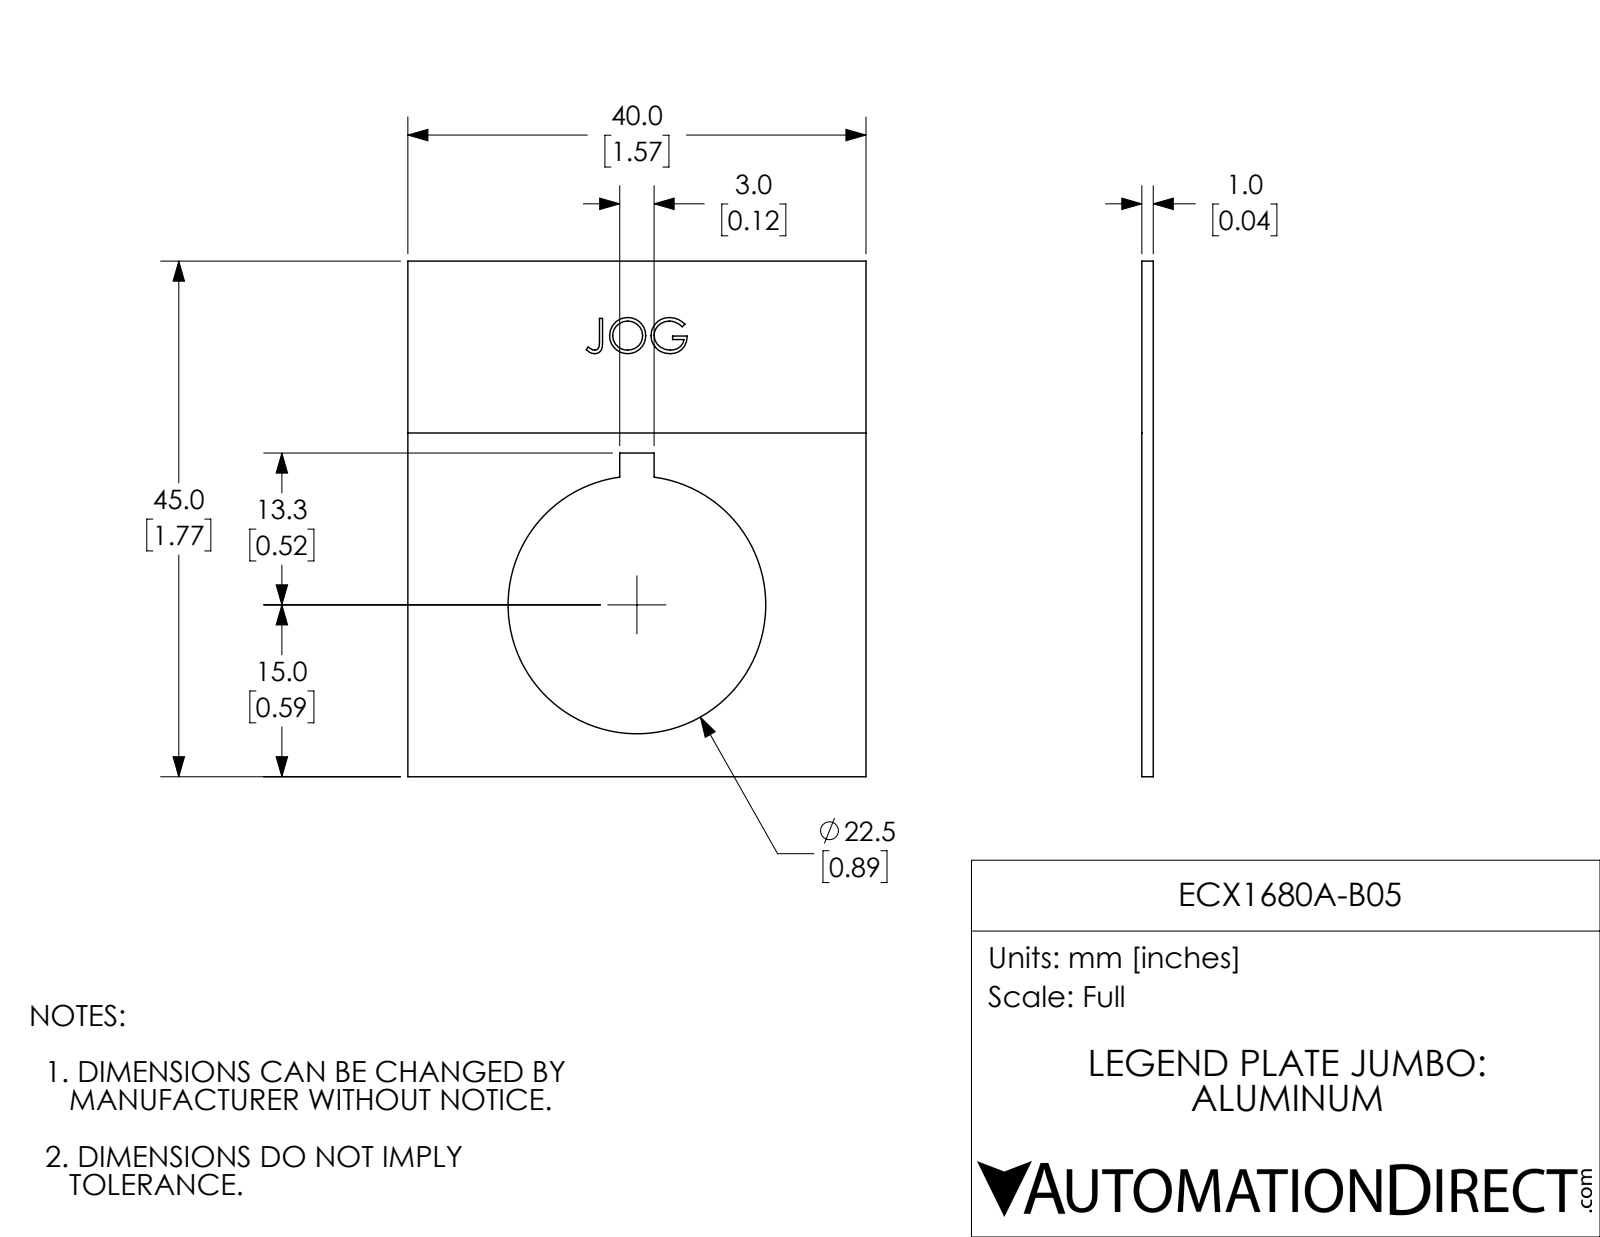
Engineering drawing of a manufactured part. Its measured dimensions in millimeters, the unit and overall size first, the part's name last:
Units: millimetres
Overall size (bounding box): 45 × 40 × 1
Round holes (diameter × count): ⌀22.5 ×1
Main face-to-face distances: 1, 0.99, 40, 45, 18.5, 21.5, 28.25, 16.75, 3, 30
Volume: 1 393 mm³ · Surface area: 3 038 mm²
Bodies: 1 solid, 48 faces (23 planar, 3 cylindrical, 22 other)
Part name (STEP PRODUCT): ECX1680A-B05
STEP written by: SolidWorks 2017 (AUTOMOTIVE_DESIGN)
